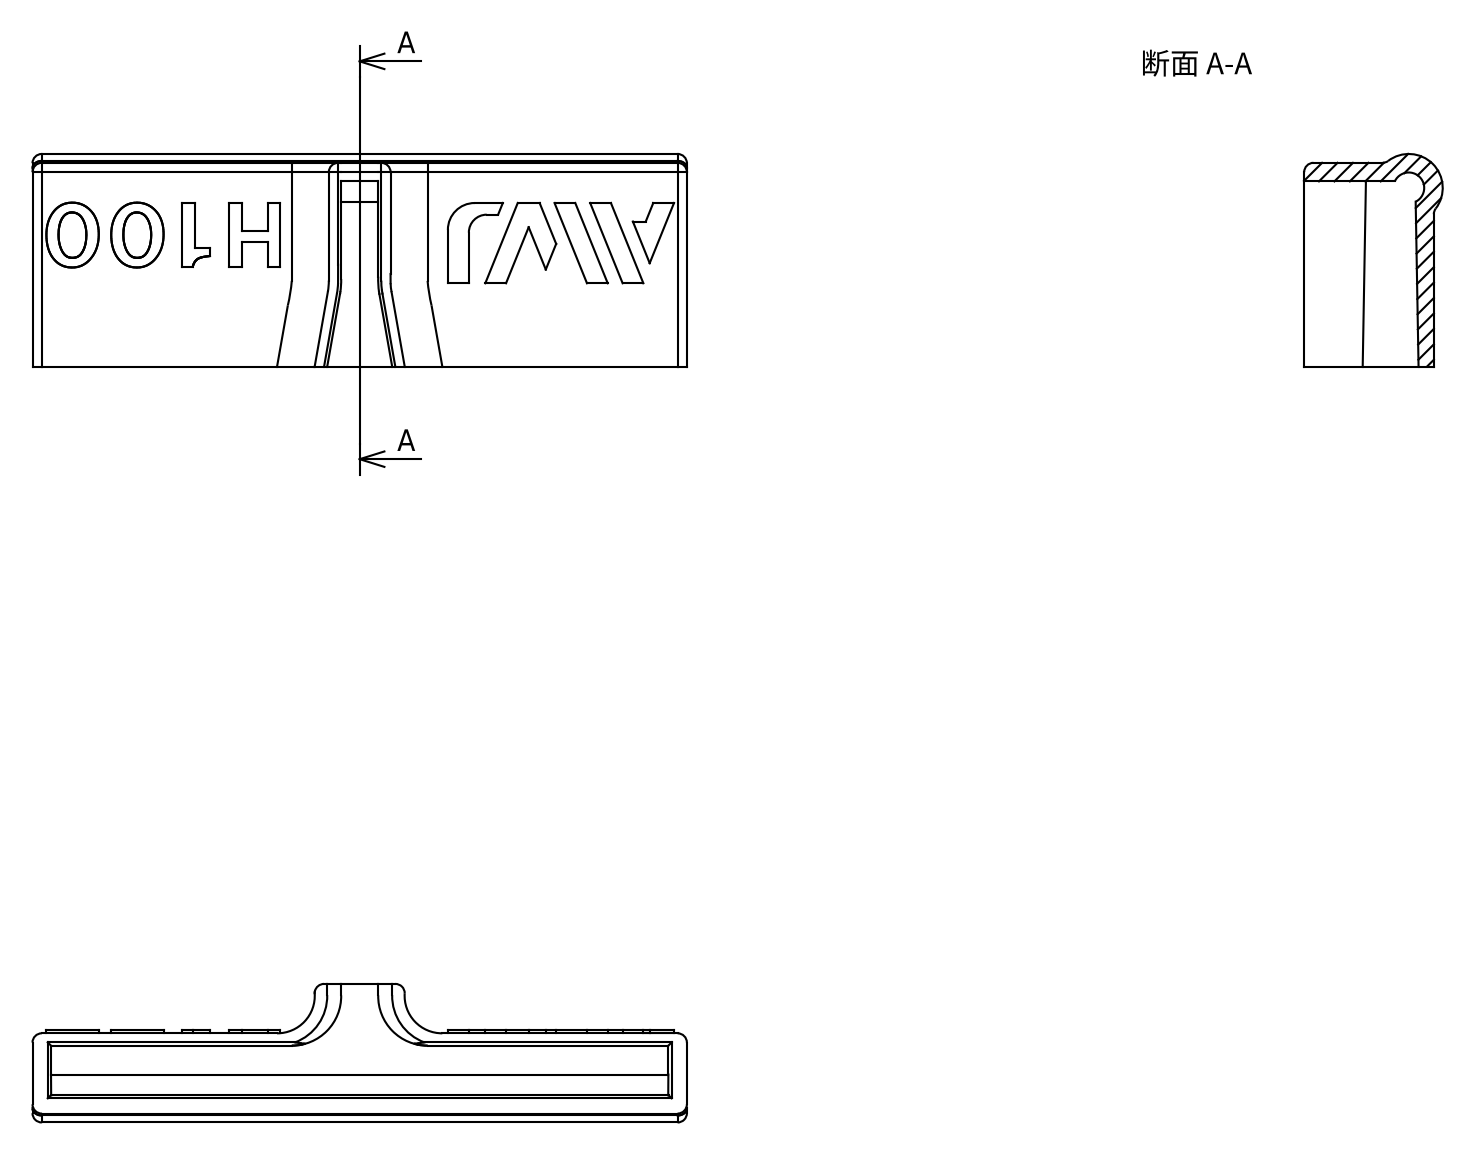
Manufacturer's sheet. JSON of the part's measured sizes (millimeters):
{"step_written_by": "Spatial InterOp 3D (CONFIG_CONTROL_DESIGN)", "units": "millimeters", "bodies": {"solids": 6, "faces": 126, "planar": 74, "cylindrical": 17, "other": 35}, "overall_size": [106, 35.48, 22.44], "volume_mm3": 21121, "surface_area_mm2": 18452, "partial_cylinders_radius": [[1.5, 10], [2.5, 1], [2.89, 1], [4.33, 1], [5.5, 1]], "face_to_face_distances": [13, 30, 13.5, 3, 0.5, 33, 106, 5.35, 3.12, 2]}
